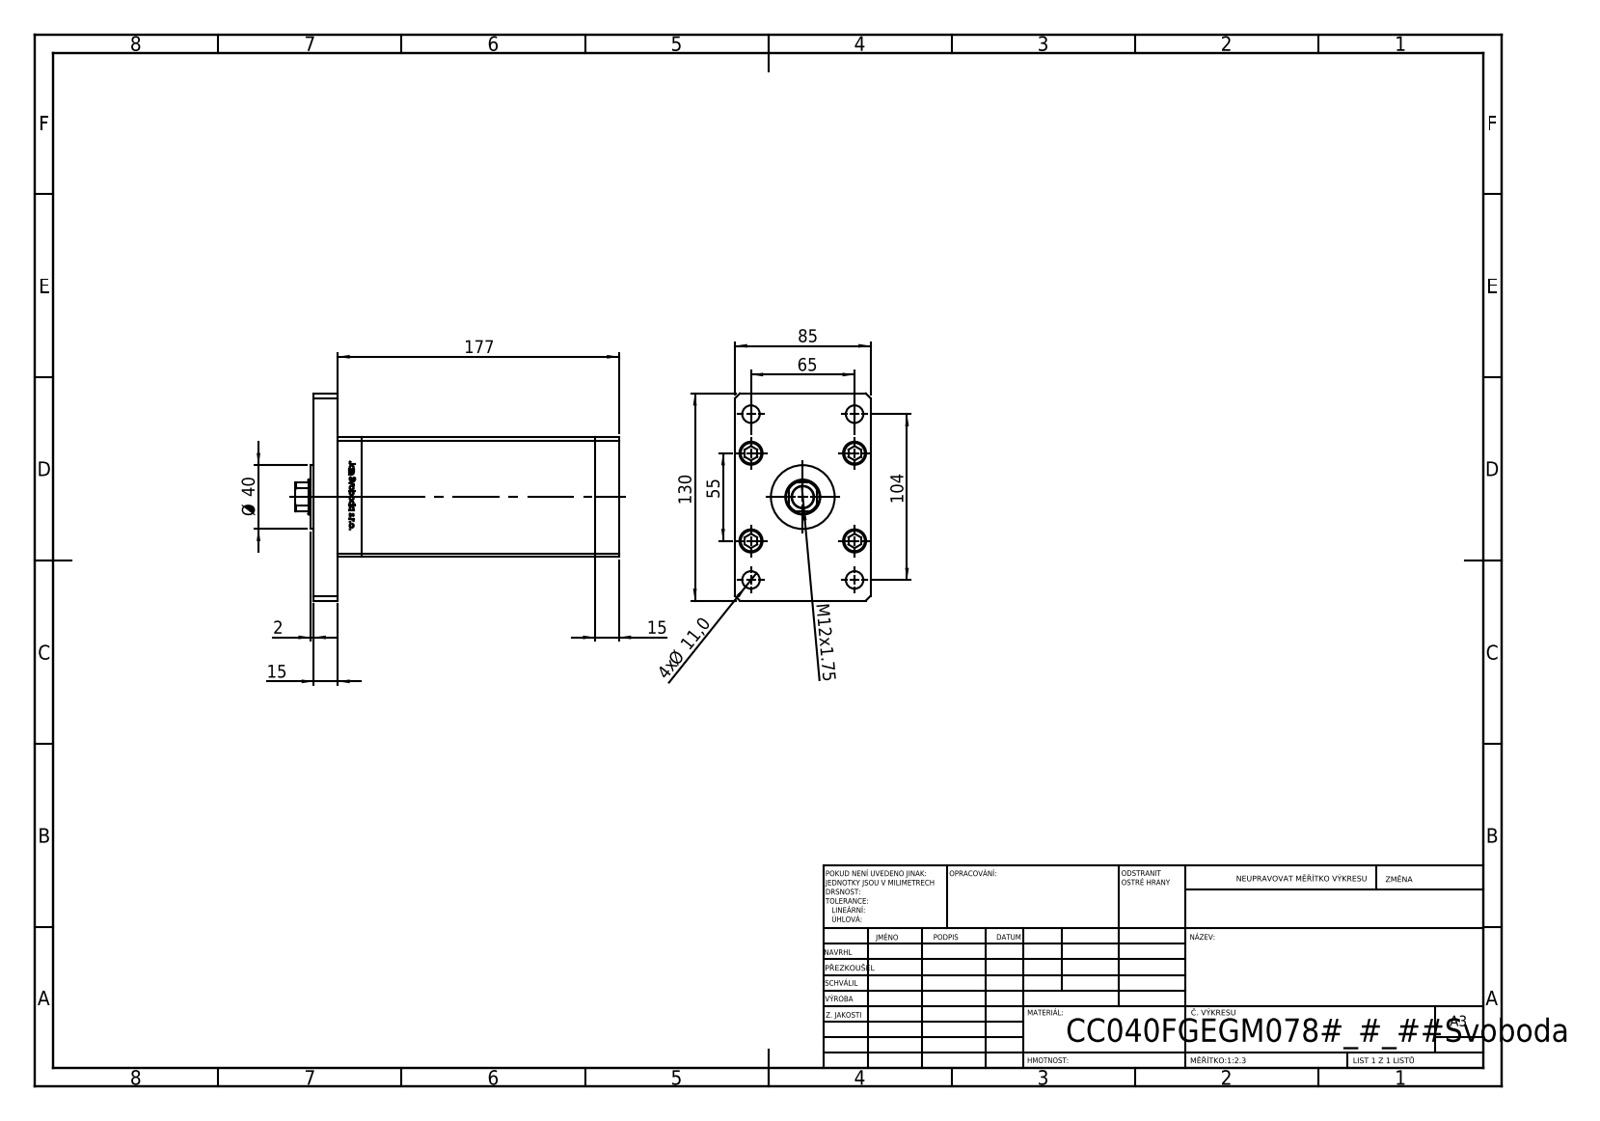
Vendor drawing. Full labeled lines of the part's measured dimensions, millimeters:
Part name (STEP PRODUCT): V220C BACK_F; ALLEN BOLT; V220C_F; V220C_F_MIDDLE (+2 more)
STEP written by: SolidWorks 2019 (CONFIG_CONTROL_DESIGN)
Units: millimetres
Bodies: 19 solids, 1310 faces (517 planar, 187 cylindrical, 606 other)
Overall size (bounding box): 203 × 130 × 85
Volume: 1 155 000 mm³ · Surface area: 197 819 mm²
Round holes (diameter × count): ⌀11 ×9, ⌀15.5 ×5, ⌀10 ×4, ⌀14.5 ×4, ⌀2 ×2, ⌀13.16 ×2, ⌀13.5 ×1, ⌀22 ×1, ⌀23.5 ×1
Round bosses / shafts (diameter × count): ⌀8 ×9, ⌀14.5 ×5, ⌀40 ×1
Partial cylindrical surfaces — rounded edges, fillets, slot ends (radius × count): R0.93 ×2, R10.5 ×1
Main face-to-face distances: 15, 85, 161.5, 176.5, 75, 30, 146.5, 191.5, 10.5, 27.5
Hole centre spacings: 28, 24.5, 42.57, 61.32, 65, 69.46, 79.5, 102.69
